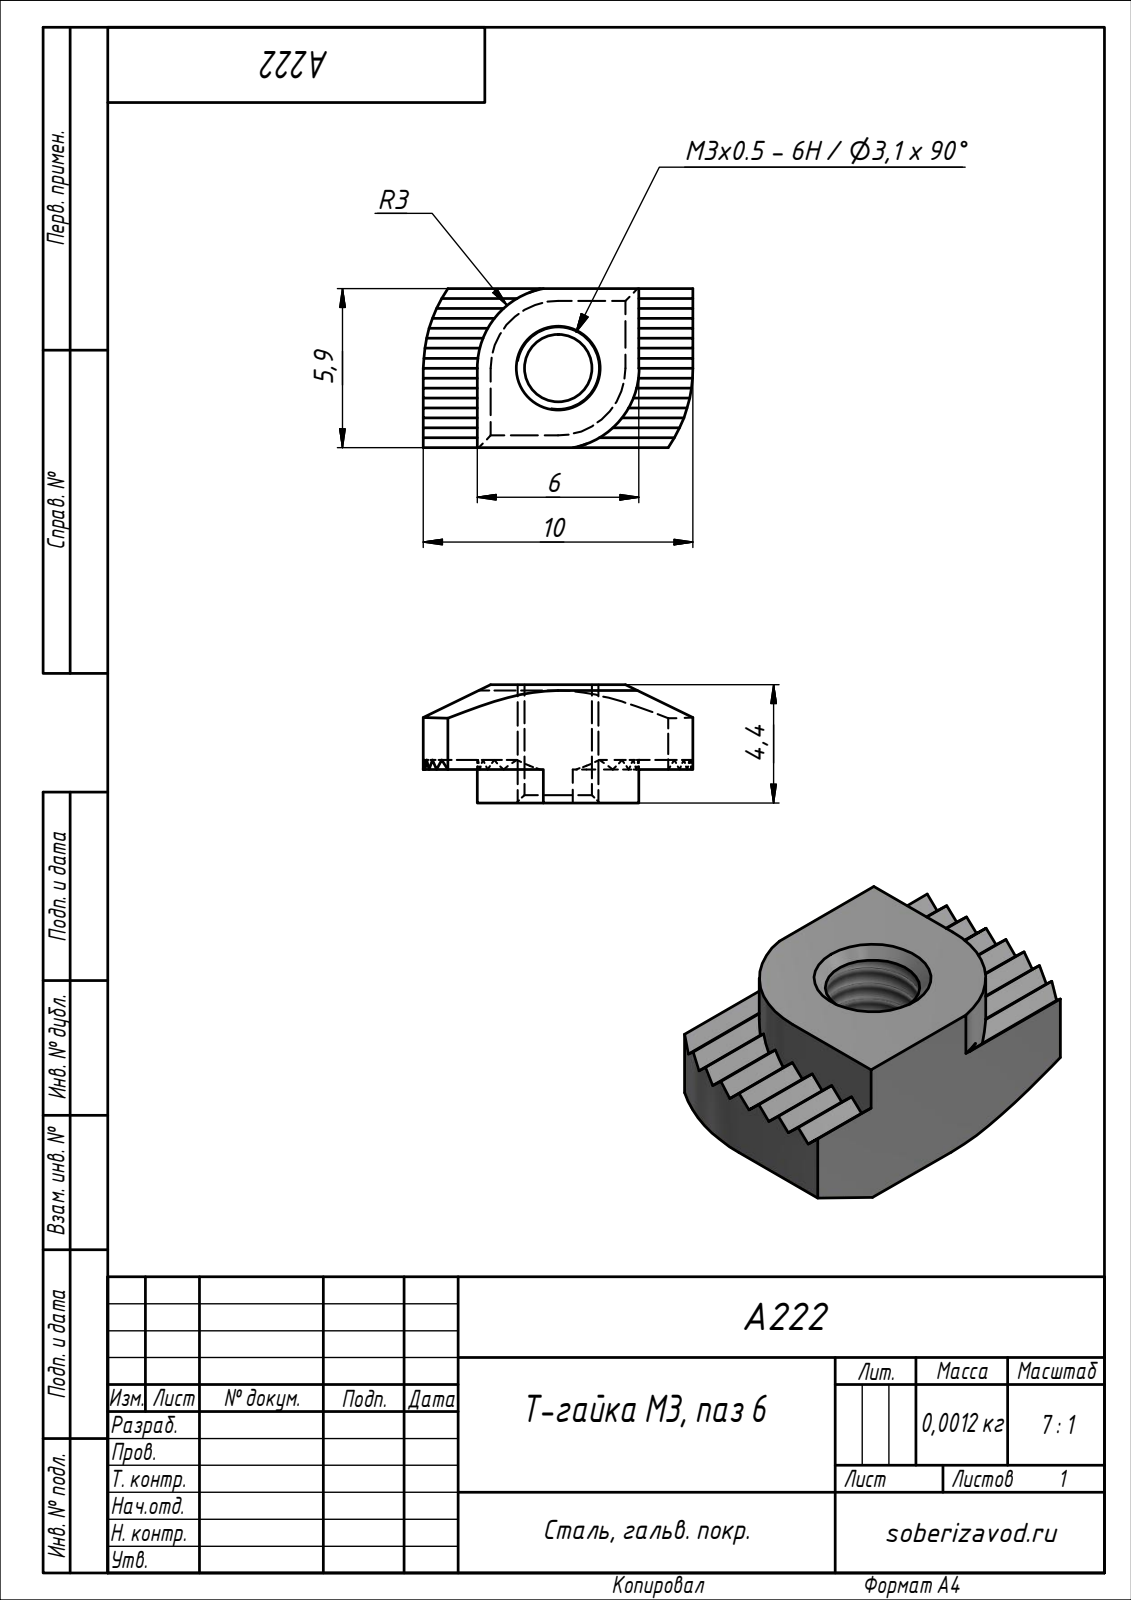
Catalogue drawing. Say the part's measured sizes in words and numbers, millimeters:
The part is named "A128 Т-гайка М3, паз 6". Its 3-D file was written by "SolidWorks 2019 (AUTOMOTIVE_DESIGN)". It is 1 solid with 58 faces: 48 planar, 6 cylindrical and 4 other. Overall it measures 10 by 5.9 by 4.4 millimeters. Its volume is 174 cubic millimeters and its surface area 250 square millimeters. Round holes: 1 of diameter 2.5. Partial cylindrical surfaces (rounded edges, fillets, slot ends): 2 of radius 5.25, 1 of radius 3. The main face-to-face distances are 5.9, 0.51, 4.4, 1.02, 2.03, 2.54, 1.52, 3.05, 2, 8.
